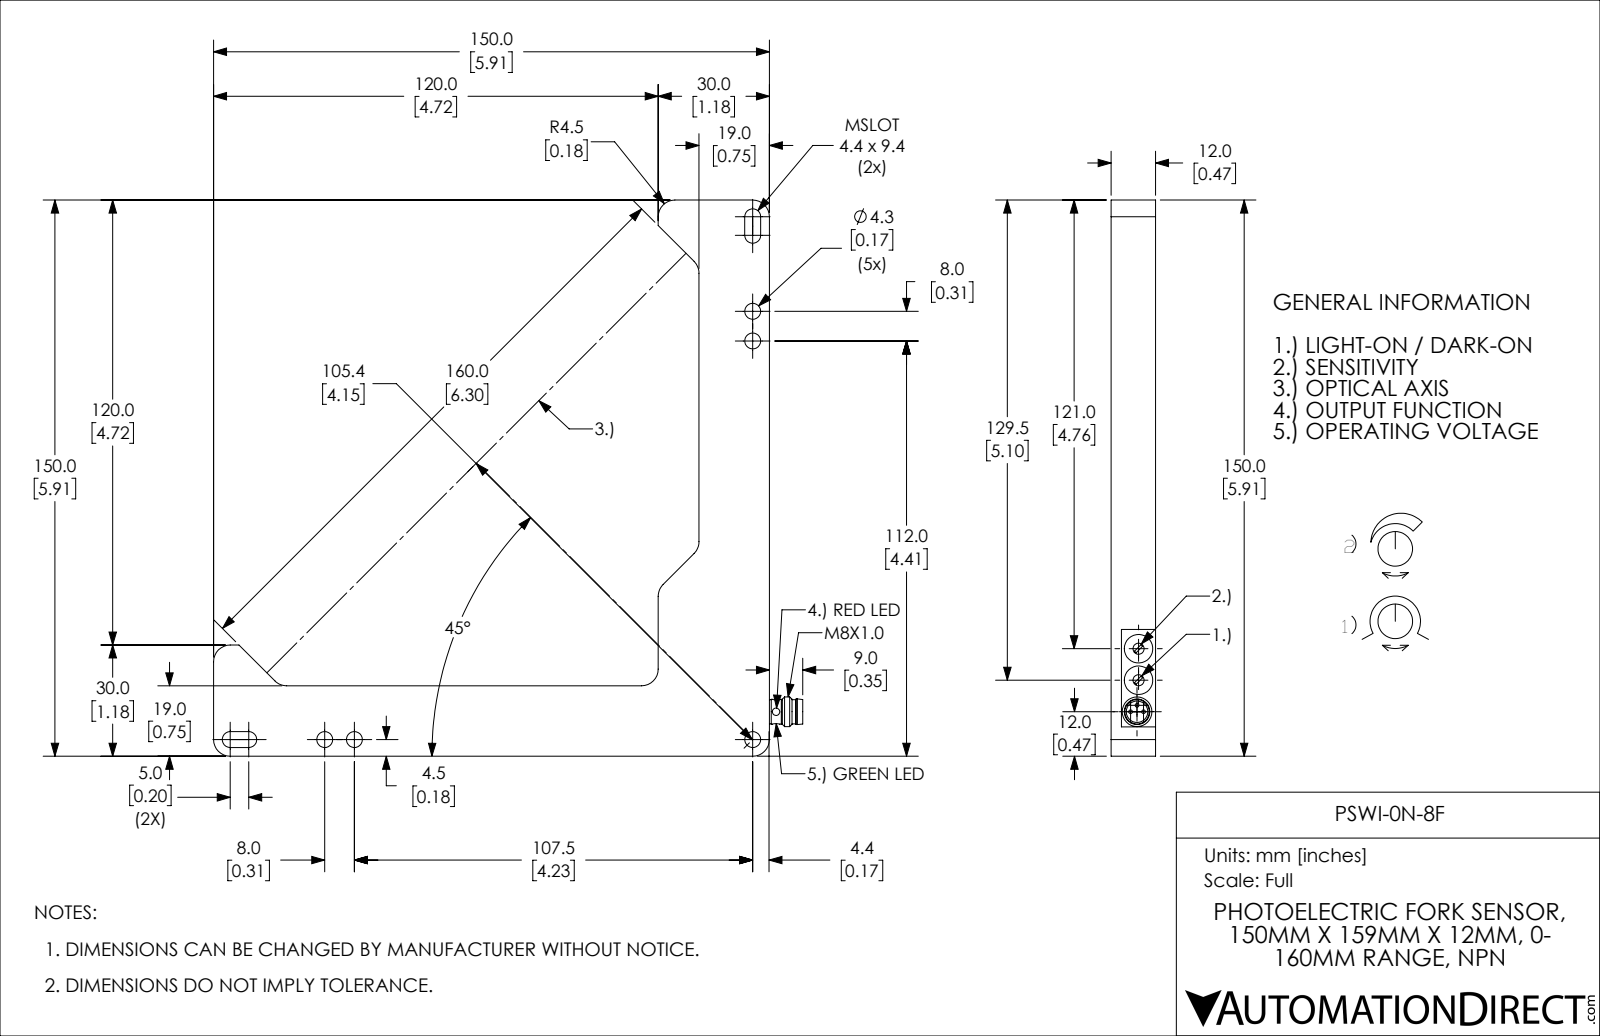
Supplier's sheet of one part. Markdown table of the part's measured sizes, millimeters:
| quantity | value |
| --- | --- |
| part name | PSWI-0N-8F |
| STEP written by | SolidWorks 2017 (AUTOMOTIVE_DESIGN) |
| units | millimeters |
| bodies | 1 solid, 90 faces (42 planar, 41 cylindrical, 7 other) |
| overall size | 159 × 150 × 12 |
| volume | 69 740 mm³ |
| surface area | 20 700 mm² |
| round holes (diameter × count) | 4.3 × 5, 2 × 2, 3 × 2, 7.7 × 2, 5.8 × 1 |
| round bosses / shafts (diameter × count) | 1 × 3, 8 × 1, 6.9 × 1, 6.7 × 1, 6.5 × 1 |
| partial cylindrical surfaces (radius × count) | 4.5 × 10, 2.2 × 4, 1.2 × 2 |
| main face-to-face distances | 12, 19, 150, 131, 30, 11, 120, 160, 2.4, 6.7 |
| hole center spacings | 8, 107.5, 115.5, 157.8, 8.5, 8.5, 9.8, 17 |
